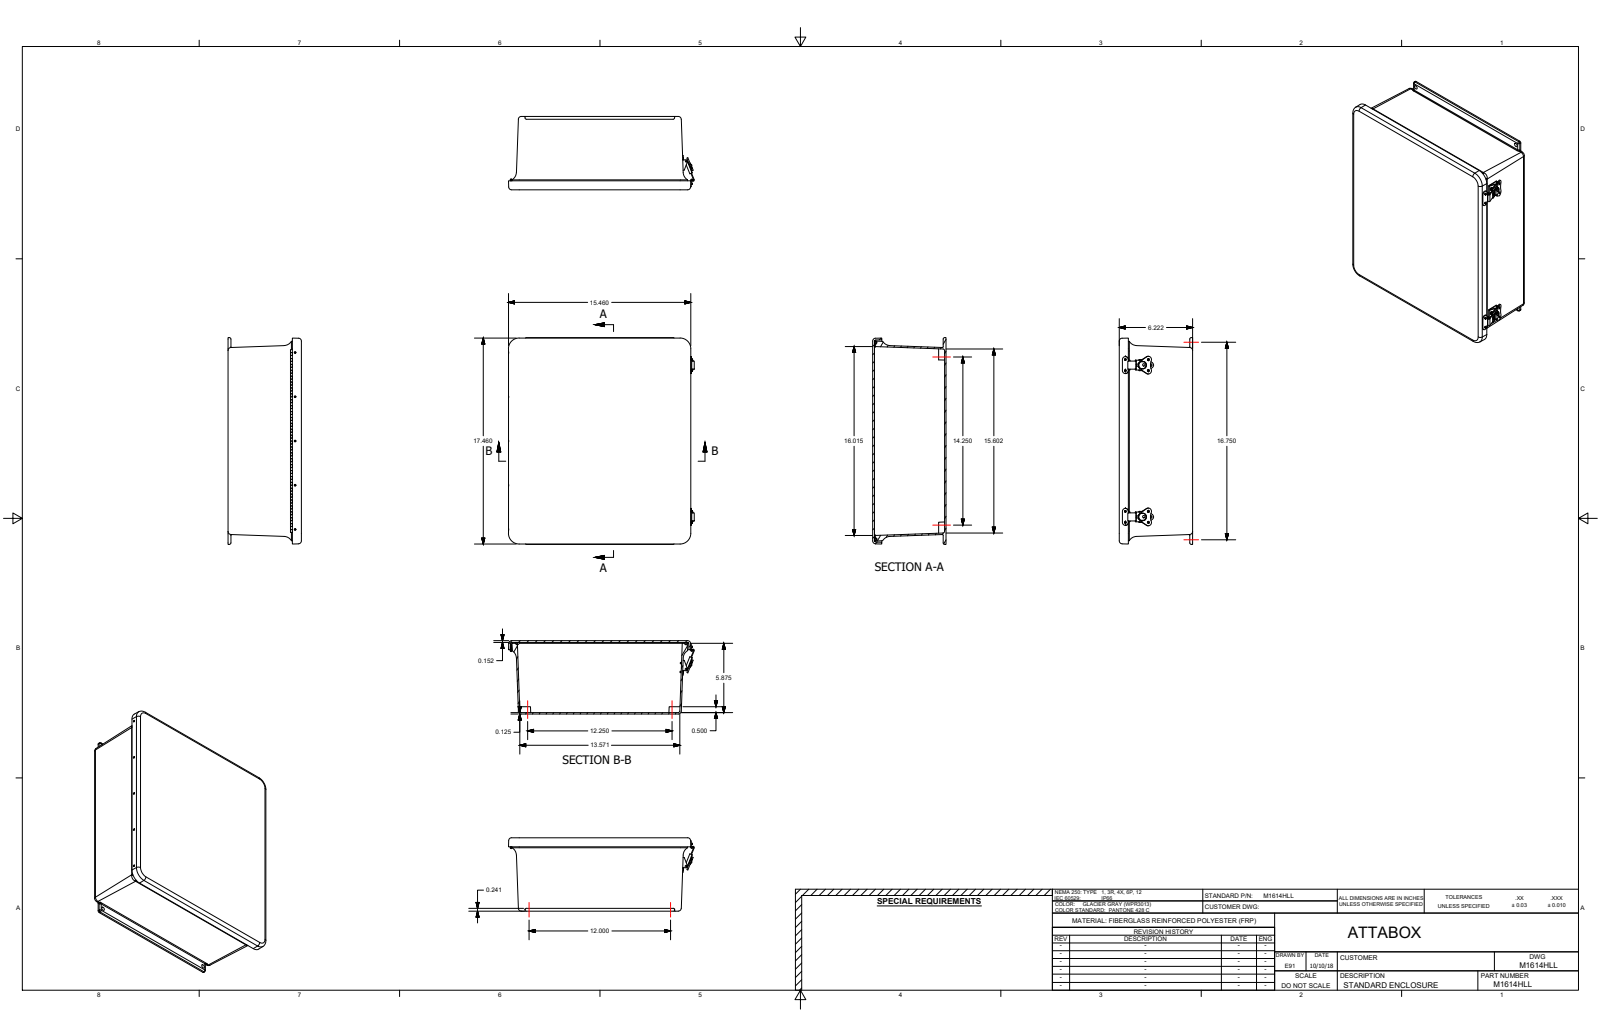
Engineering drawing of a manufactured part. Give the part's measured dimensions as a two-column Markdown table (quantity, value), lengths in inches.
| quantity | value |
| --- | --- |
| part name | M1614HLL |
| STEP written by | SolidWorks 2018 (AUTOMOTIVE_DESIGN) |
| units | inches |
| bodies | 44 solids, 1090 faces (527 planar, 445 cylindrical, 118 other) |
| overall size | 17.53 × 15.741 × 6.222 |
| volume | 144.4 in³ |
| surface area | 1 973 in² |
| round holes (diameter × count) | 0.14 × 20, 0.104 × 18, 0.131 × 10, 0.152 × 8, 0.13 × 4, 0.133 × 4, 0.187 × 4, 0.191 × 4, 0.218 × 4, 0.312 × 4, 0.135 × 2, 0.189 × 2 |
| round bosses / shafts (diameter × count) | 0.125 × 12, 0.125 × 8, 0.66 × 2, 0.582 × 2, 0.525 × 2, 0.286 × 2, 0.213 × 2, 0.18 × 2 |
| partial cylindrical surfaces (radius × count) | 0.125 × 17, 0.015 × 16, 0.06 × 13, 0.25 × 10, 0.011 × 8, 0.02 × 8, 0.055 × 8, 0.07 × 8 |
| main face-to-face distances | 0.125, 0.152, 6.222, 6.07, 6.097, 5.944, 0.125, 0.222, 0.07, 5.875 |
| hole center spacings | 3.75, 7.5, 11.25, 12.868, 12.869, 0.25, 3.25, 3.5 |
